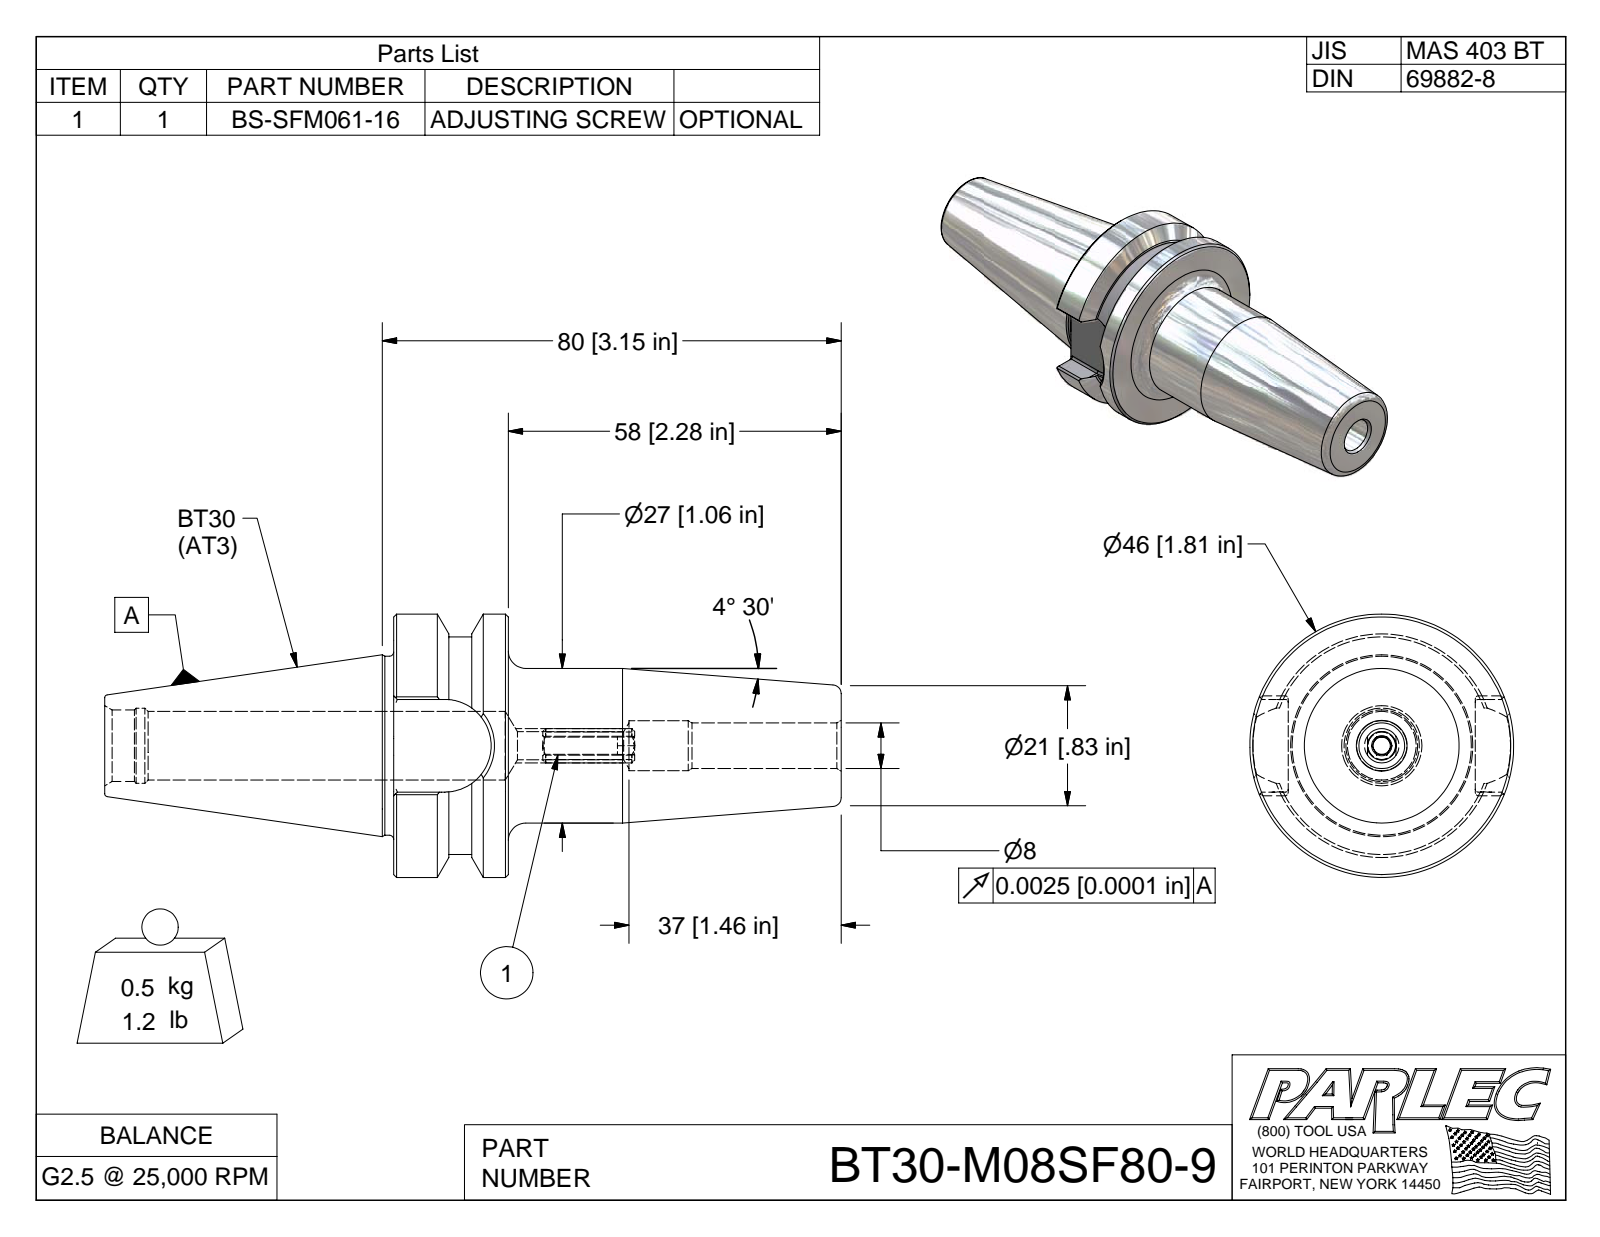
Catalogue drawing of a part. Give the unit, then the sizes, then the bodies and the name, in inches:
Units: inches
Overall size (bounding box): 5.056 × 1.811 × 1.811
Round holes (diameter × count): ⌀0.314 ×1, ⌀0.344 ×1, ⌀0.517 ×1
Round bosses / shafts (diameter × count): ⌀1.811 ×1, ⌀1.23 ×1, ⌀1.063 ×1
Partial cylindrical surfaces — rounded edges, fillets, slot ends (radius × count): R0.02 ×8, R0.118 ×1, R0.319 ×1, R0.748 ×1
Main face-to-face distances: 0.787, 1.283, 3.072, 2.285, 0.543, 0.74, 1.984, 2.771, 5.056, 0.637
Volume: 4.379 in³ · Surface area: 28.83 in²
Bodies: 2 solids, 97 faces (35 planar, 22 cylindrical, 40 other)
Part name (STEP PRODUCT): BT30-M08SF80-9; BT30-M08SF80-9-1; BS-SFM061-16
STEP written by: Autodesk Inventor 2009 (AUTOMOTIVE_DESIGN)
